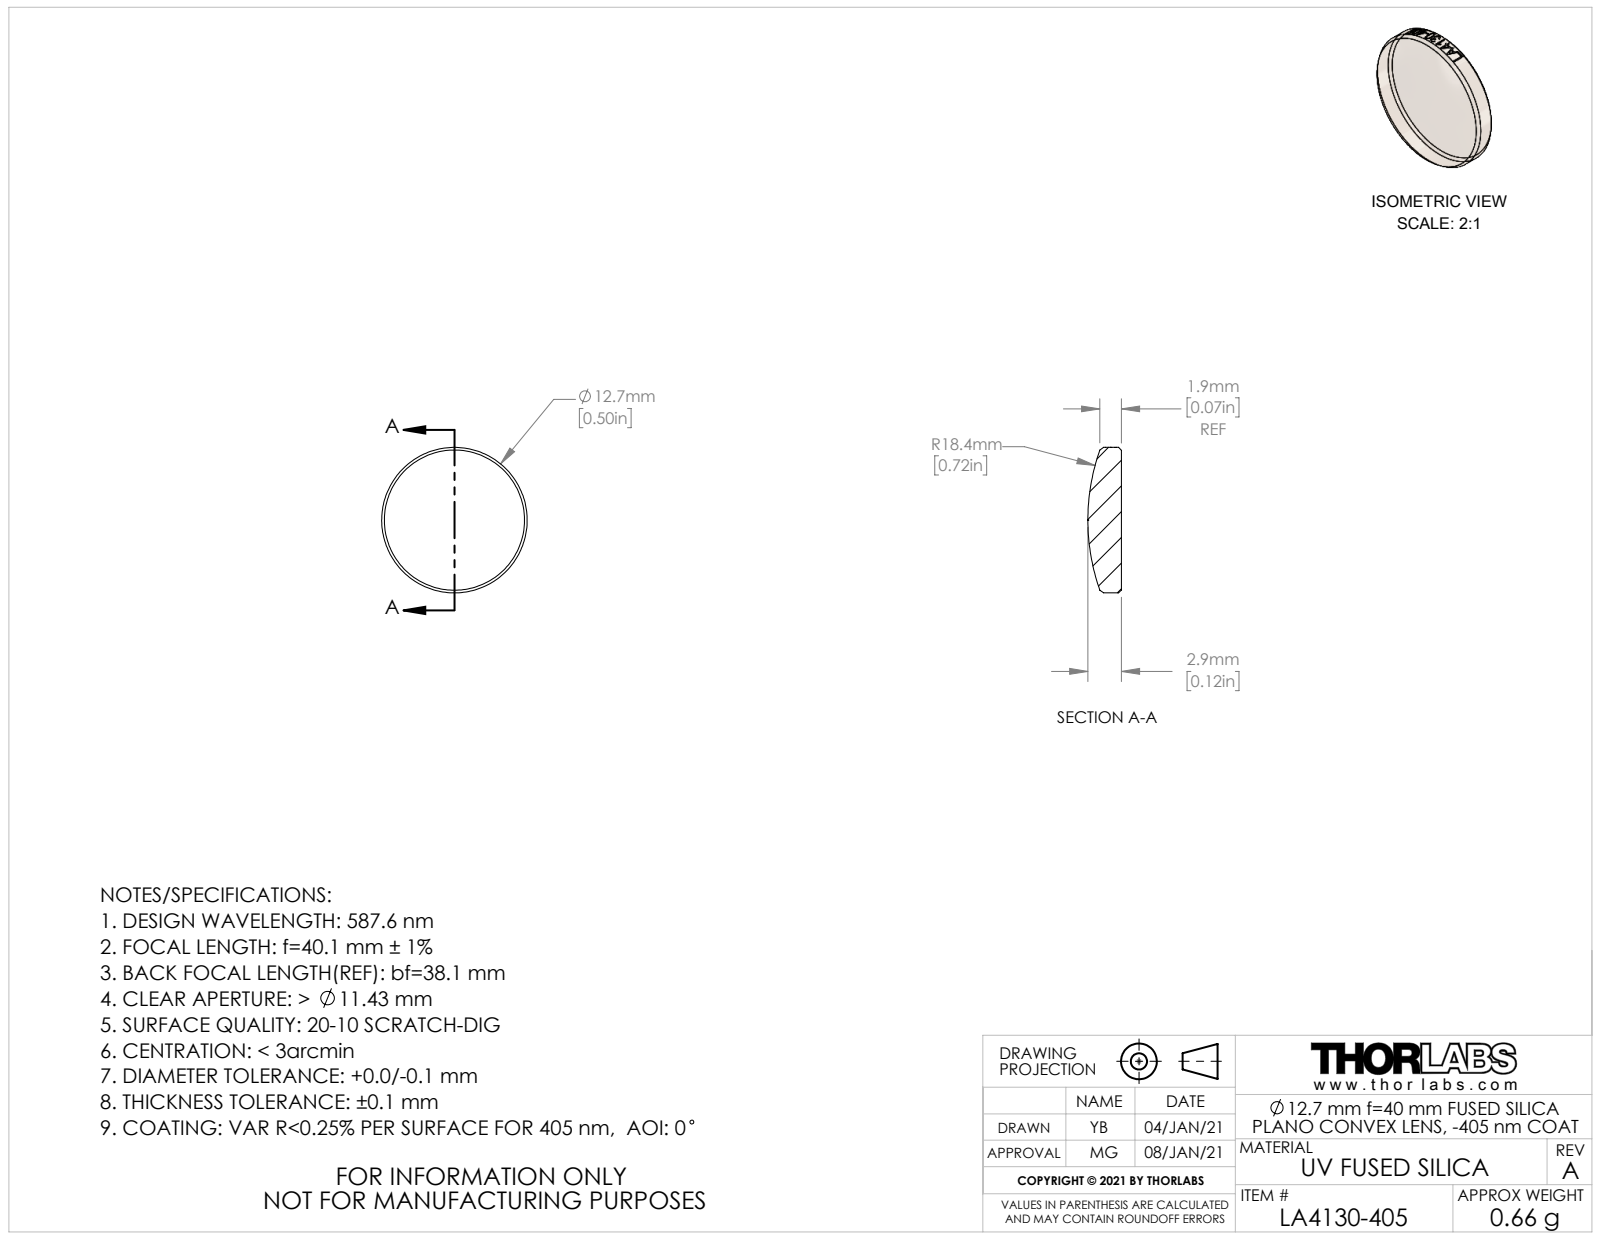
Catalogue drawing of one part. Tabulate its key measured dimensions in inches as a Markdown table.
| quantity | value |
| --- | --- |
| part name | CTN016826-E0W; CTN016846 |
| STEP written by | SolidWorks 2018 (AUTOMOTIVE_DESIGN) |
| units | inches |
| bodies | 1 solid, 30 faces (1 planar, 23 cylindrical, 6 other) |
| overall size | 0.5 × 0.5 × 0.115 |
| volume | 0.018 in³ |
| surface area | 0.495 in² |
| round bosses / shafts (diameter × count) | 0.5 × 1 |
